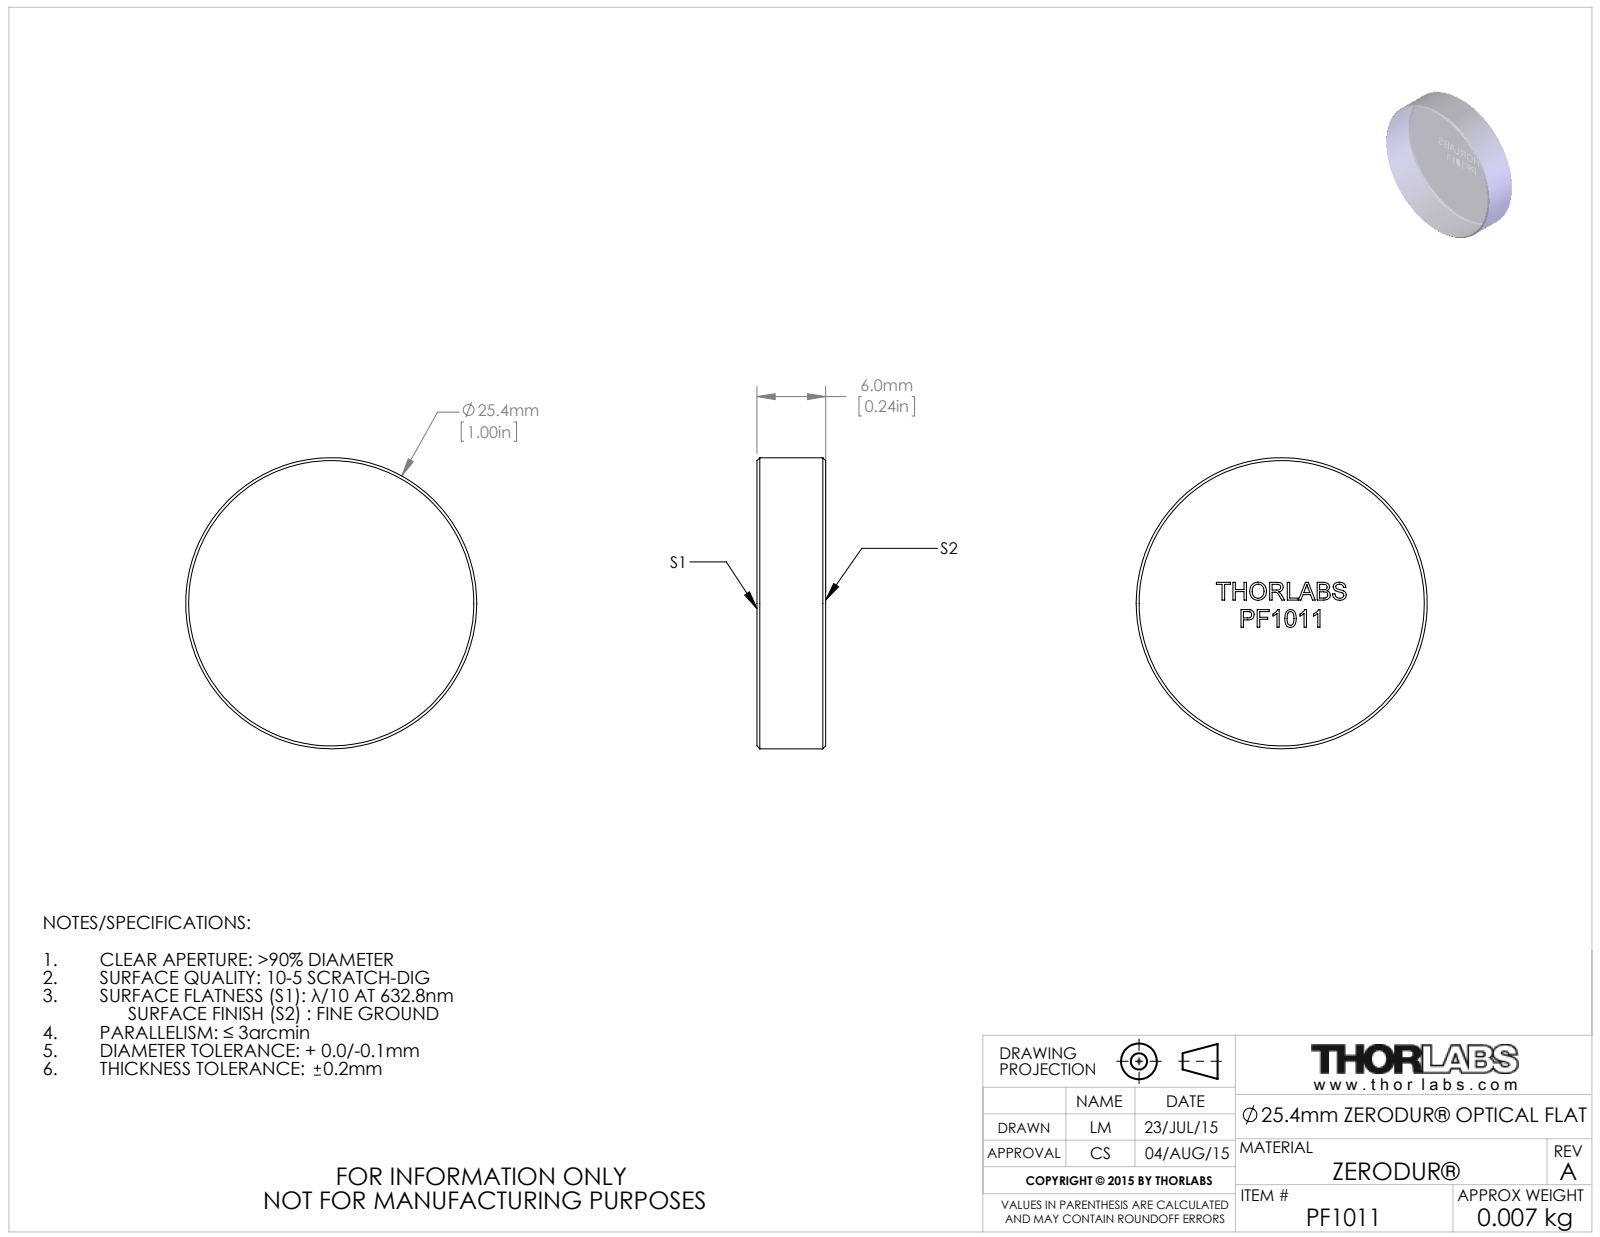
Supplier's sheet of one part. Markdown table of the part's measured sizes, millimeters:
| quantity | value |
| --- | --- |
| part name | TTN045229-E0W |
| STEP written by | SolidWorks 2014 (CONFIG_CONTROL_DESIGN) |
| units | millimeters |
| bodies | 1 solid, 185 faces (115 planar, 2 cylindrical, 68 other) |
| overall size | 25.4 × 25.4 × 6 |
| volume | 3 035 mm³ |
| surface area | 1 469 mm² |
| round bosses / shafts (diameter × count) | 25.4 × 1 |
| main face-to-face distances | 6, 2.37, 1.54, 4.04, 0.7, 1.19, 4.15, 1.36, 1.92, 0.73 |
